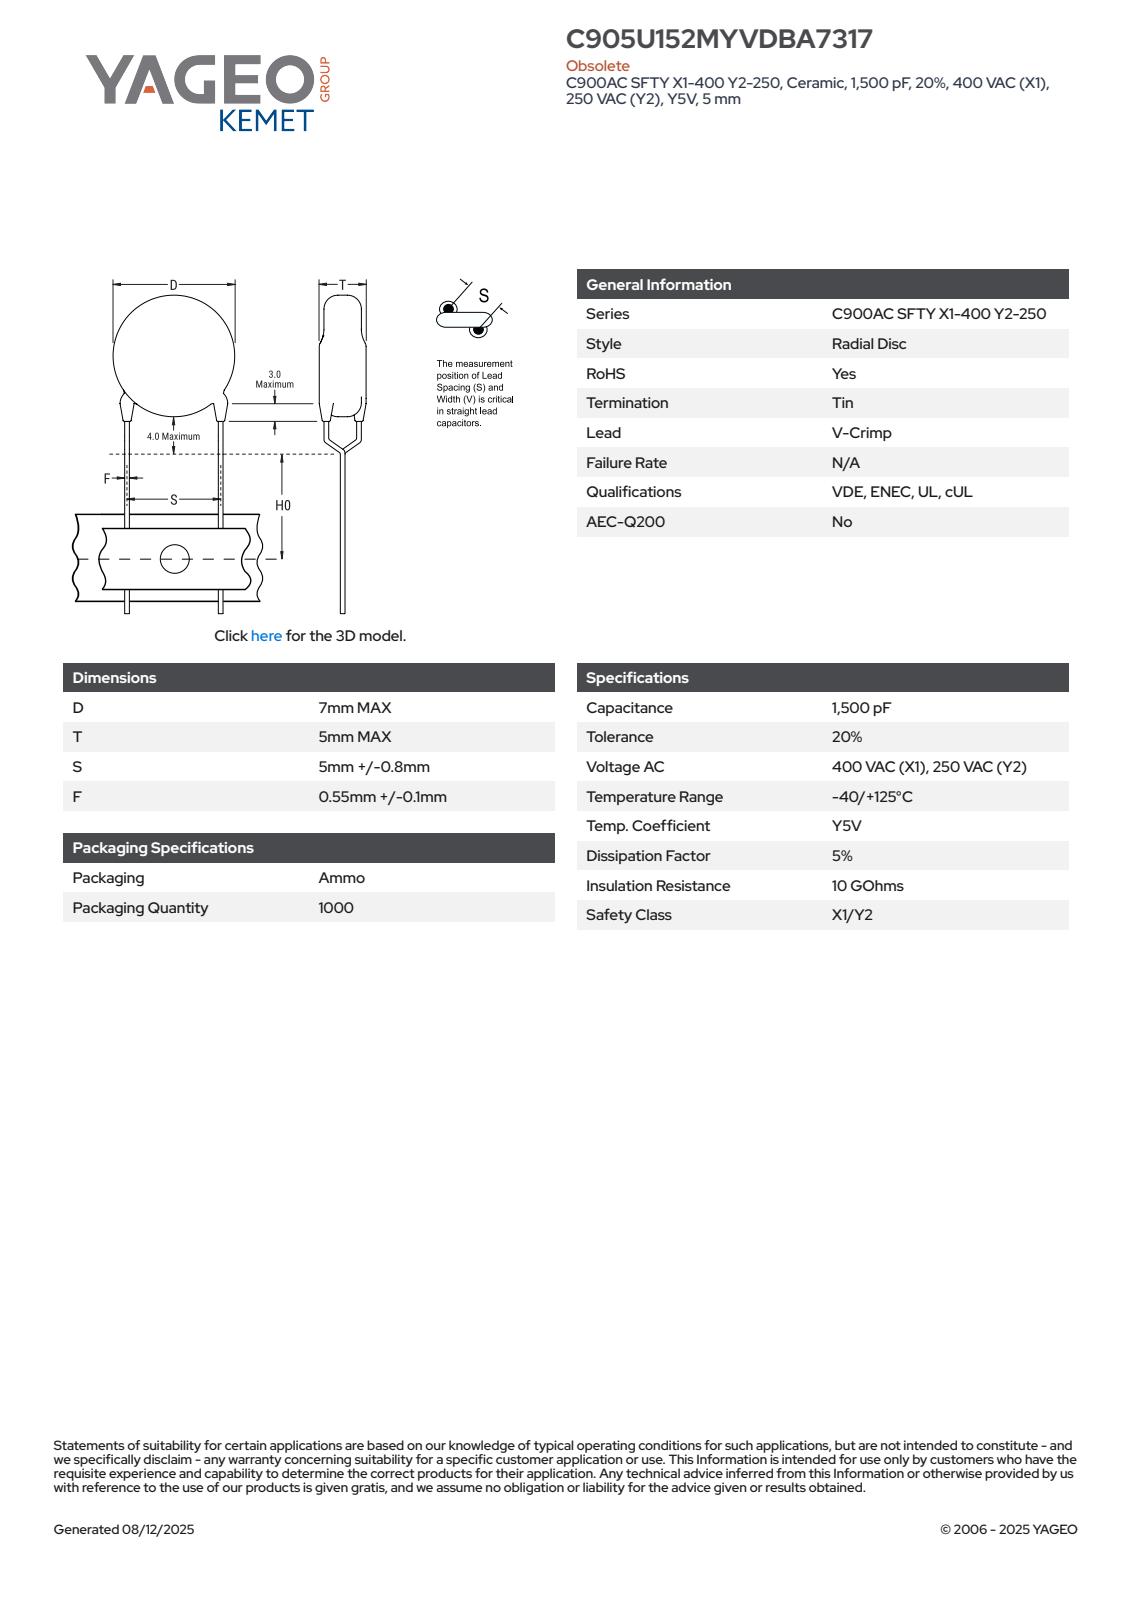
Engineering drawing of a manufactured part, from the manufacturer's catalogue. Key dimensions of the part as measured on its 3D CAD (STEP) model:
Part name (STEP PRODUCT): CCD_VCC900_D7T5S5LL20F0.65
STEP written by: SolidWorks 2014 (AUTOMOTIVE_DESIGN)
Units: millimetres
Bodies: 5 solids, 93 faces (65 planar, 16 cylindrical, 12 other)
Overall size (bounding box): 30.8 × 7 × 5
Volume: 201 mm³ · Surface area: 277 mm²
Round bosses / shafts (diameter × count): ⌀0.65 ×6, ⌀7 ×1
Main face-to-face distances: 5, 22.9, 0.91, 27.75, 4.85, 26.84, 3.94, 3.71, 0.34, 1.87
